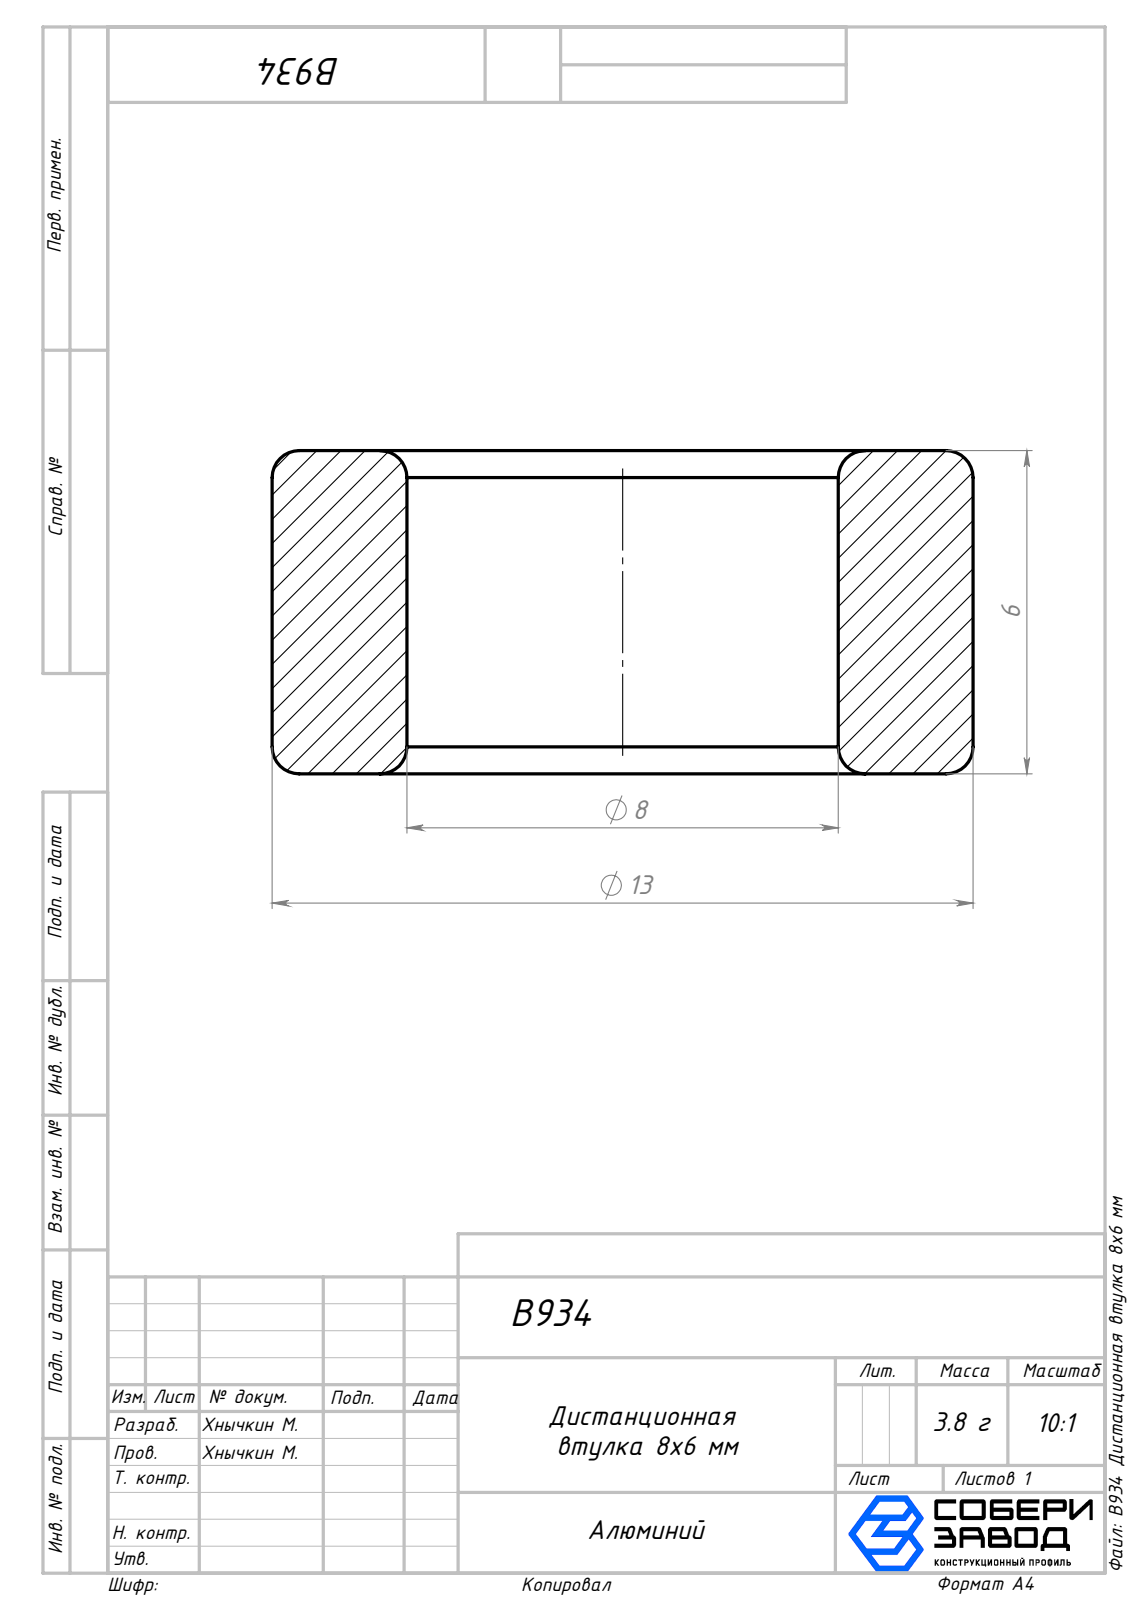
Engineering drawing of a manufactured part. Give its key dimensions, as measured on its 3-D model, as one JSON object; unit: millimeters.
{"part_name": "B934 Дистанционная втулка 8x6 мм", "step_written_by": "SolidWorks 2026 (AUTOMOTIVE_DESIGN)", "units": "millimeters", "bodies": {"solids": 1, "faces": 14, "planar": 2, "cylindrical": 4, "other": 8}, "overall_size": [13, 13, 6], "volume_mm3": 488, "surface_area_mm2": 532, "round_holes": [[8, 1]], "round_bosses_or_shafts": [[13, 1]], "face_to_face_distances": [6]}
